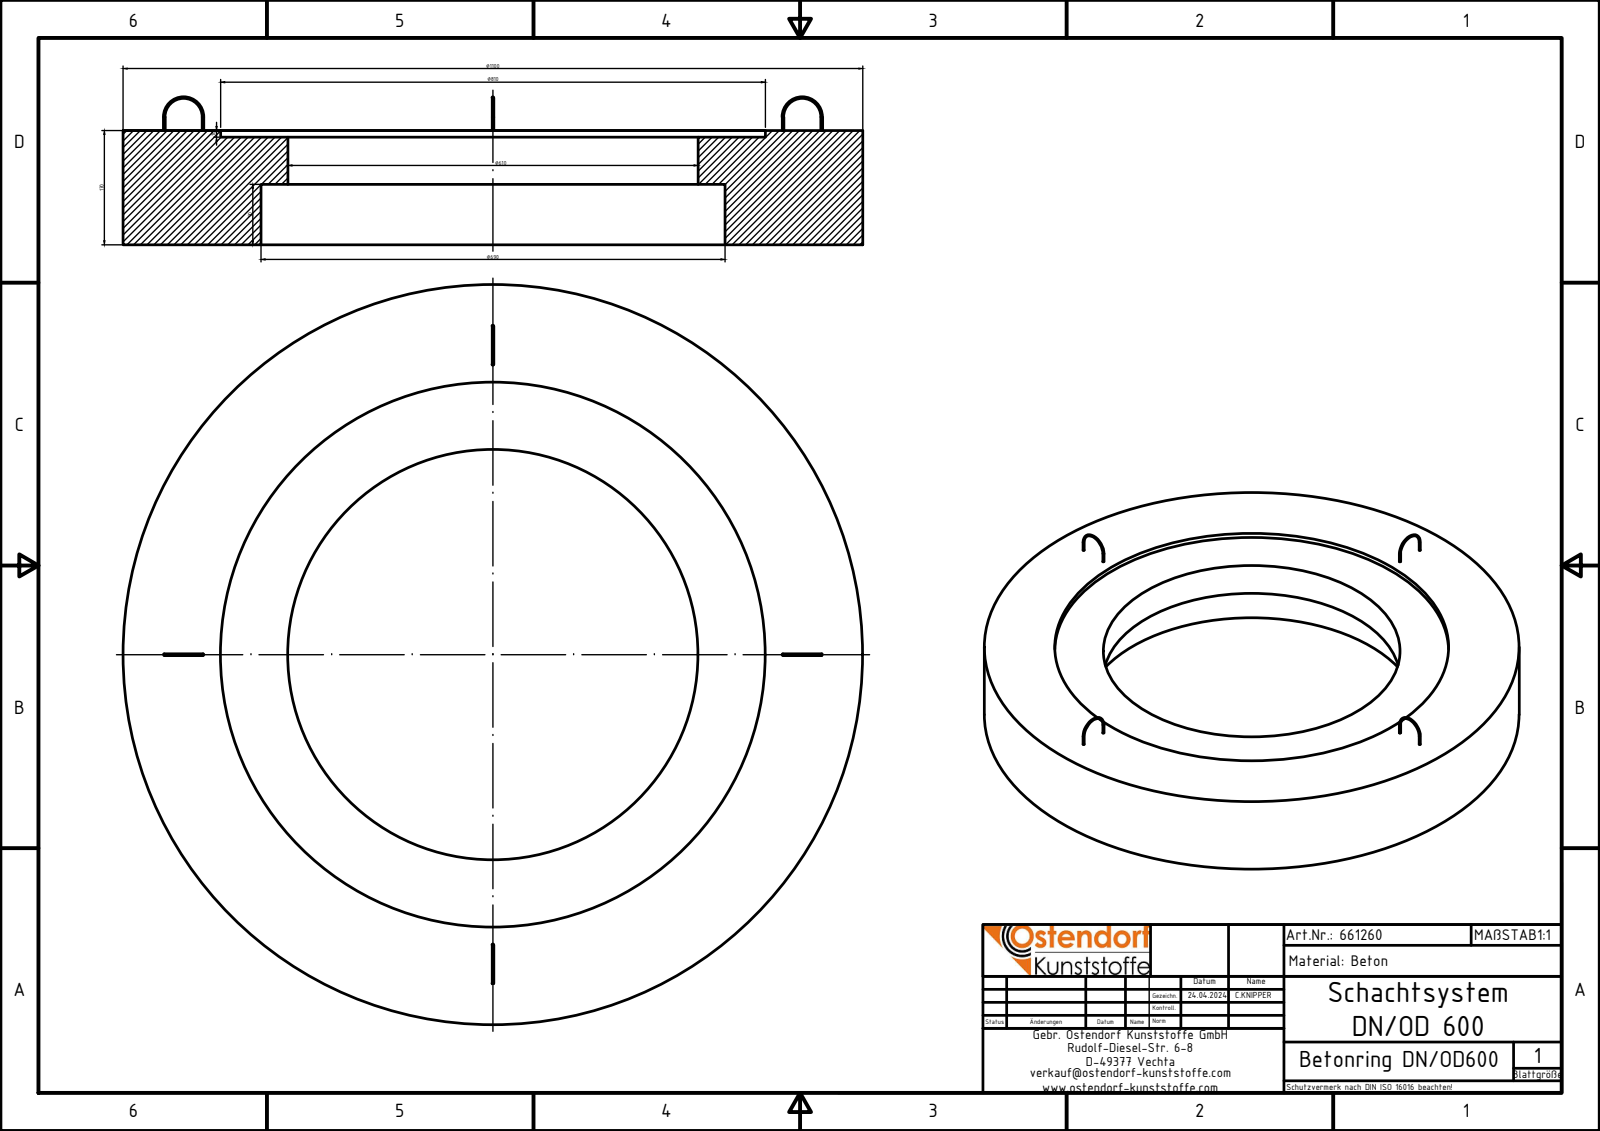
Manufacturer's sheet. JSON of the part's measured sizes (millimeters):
{"part_name": "661260z", "step_written_by": "Autodesk Inventor 2024 (AUTOMOTIVE_DESIGN)", "units": "millimeters", "bodies": {"solids": 1, "faces": 20, "planar": 4, "cylindrical": 12, "other": 4}, "overall_size": [1100, 1100, 220], "volume_mm3": 102300000, "surface_area_mm2": 2262000, "round_holes": [[610, 1], [690, 1], [810, 1]], "round_bosses_or_shafts": [[2.5, 8], [1100, 1]], "face_to_face_distances": [170, 160, 10, 90, 70, 80]}
